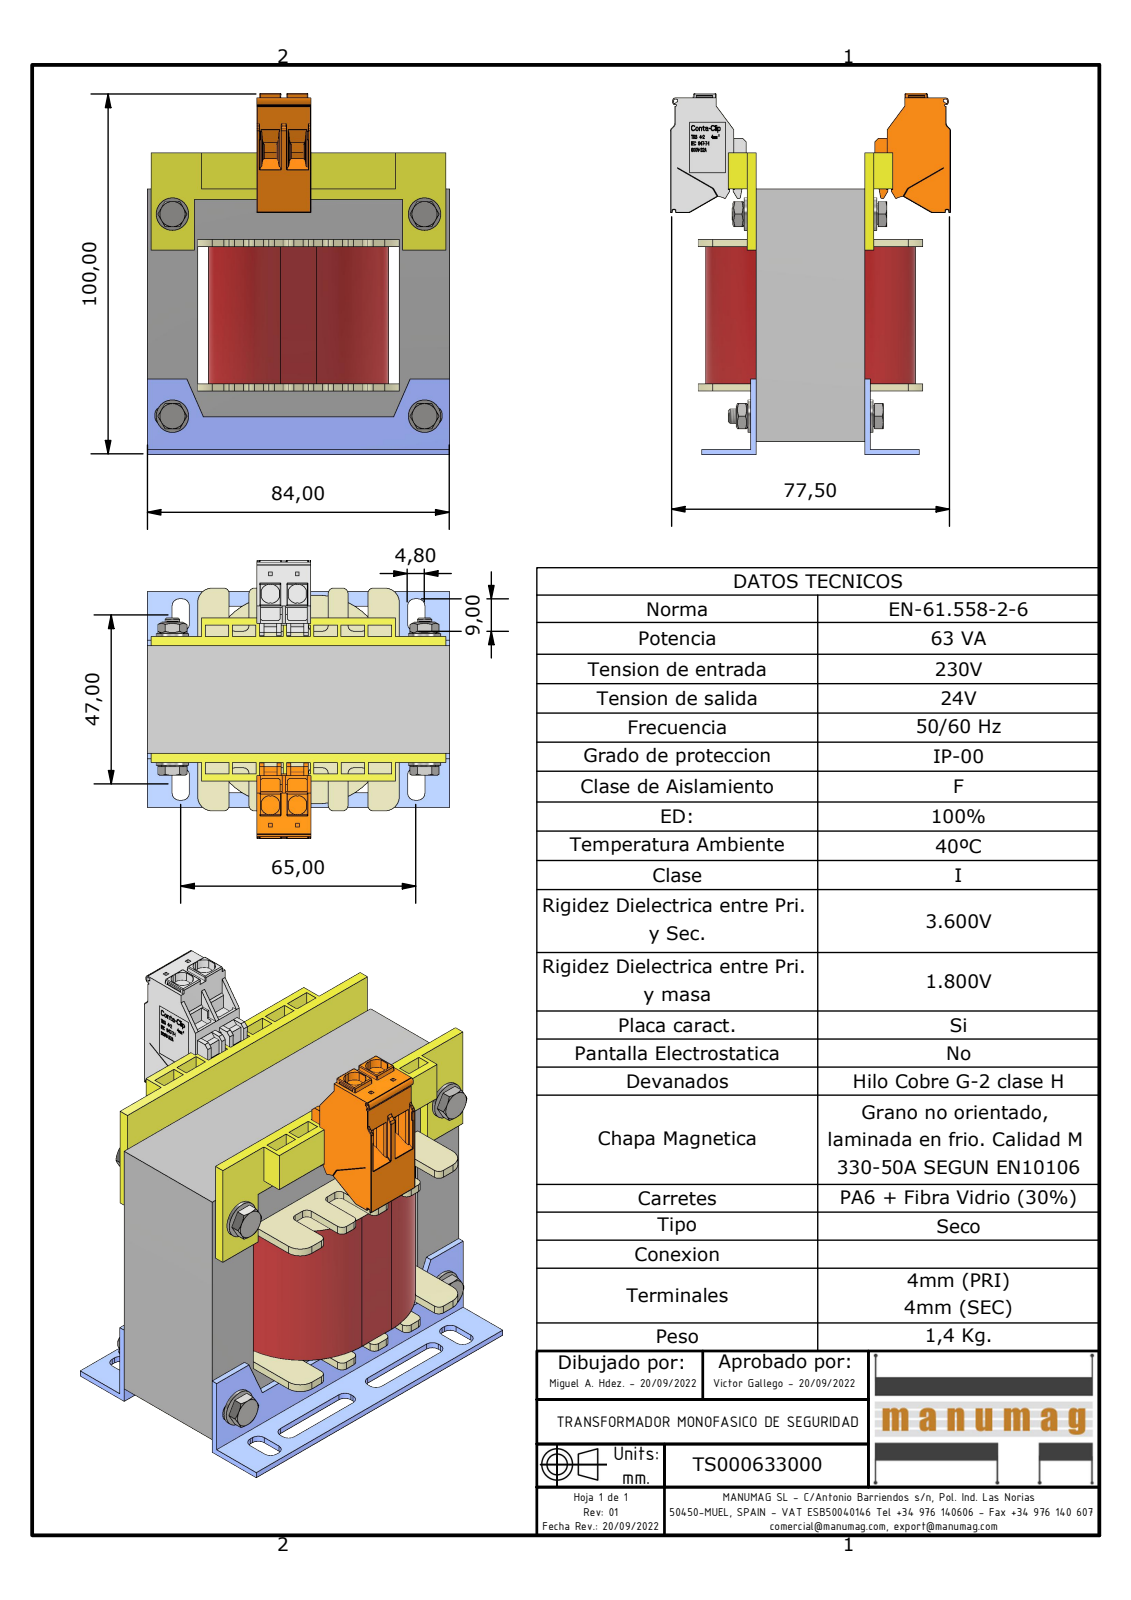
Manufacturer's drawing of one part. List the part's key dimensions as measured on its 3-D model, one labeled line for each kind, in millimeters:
Part name (STEP PRODUCT): TS000633000; EI84 x 70 - 30 (RC28); AF28DIN; EI 84 X 70 - 30 (+6 more)
STEP written by: Autodesk Inventor 2023 (AUTOMOTIVE_DESIGN)
Units: millimetres
Bodies: 24 solids, 3806 faces (3050 planar, 522 cylindrical, 234 other)
Overall size (bounding box): 100.2 × 84 × 77.4
Volume: 240 452 mm³ · Surface area: 81 418 mm²
Round holes (diameter × count): ⌀3.24 ×4, ⌀4.3 ×4, ⌀4.5 ×4, ⌀4 ×2
Round bosses / shafts (diameter × count): ⌀9 ×4, ⌀5.9 ×4, ⌀3.62 ×4, ⌀4 ×2
Partial cylindrical surfaces — rounded edges, fillets, slot ends (radius × count): R0.15 ×162, R0.2 ×60, R2 ×40, R1.5 ×32, R0.5 ×16, R0.3 ×14, R1 ×8, R1.1 ×4
Main face-to-face distances: 14, 56, 30, 28, 42, 70, 1.5, 2, 32.5, 2.5
Hole centre spacings: 56, 70, 89.64
